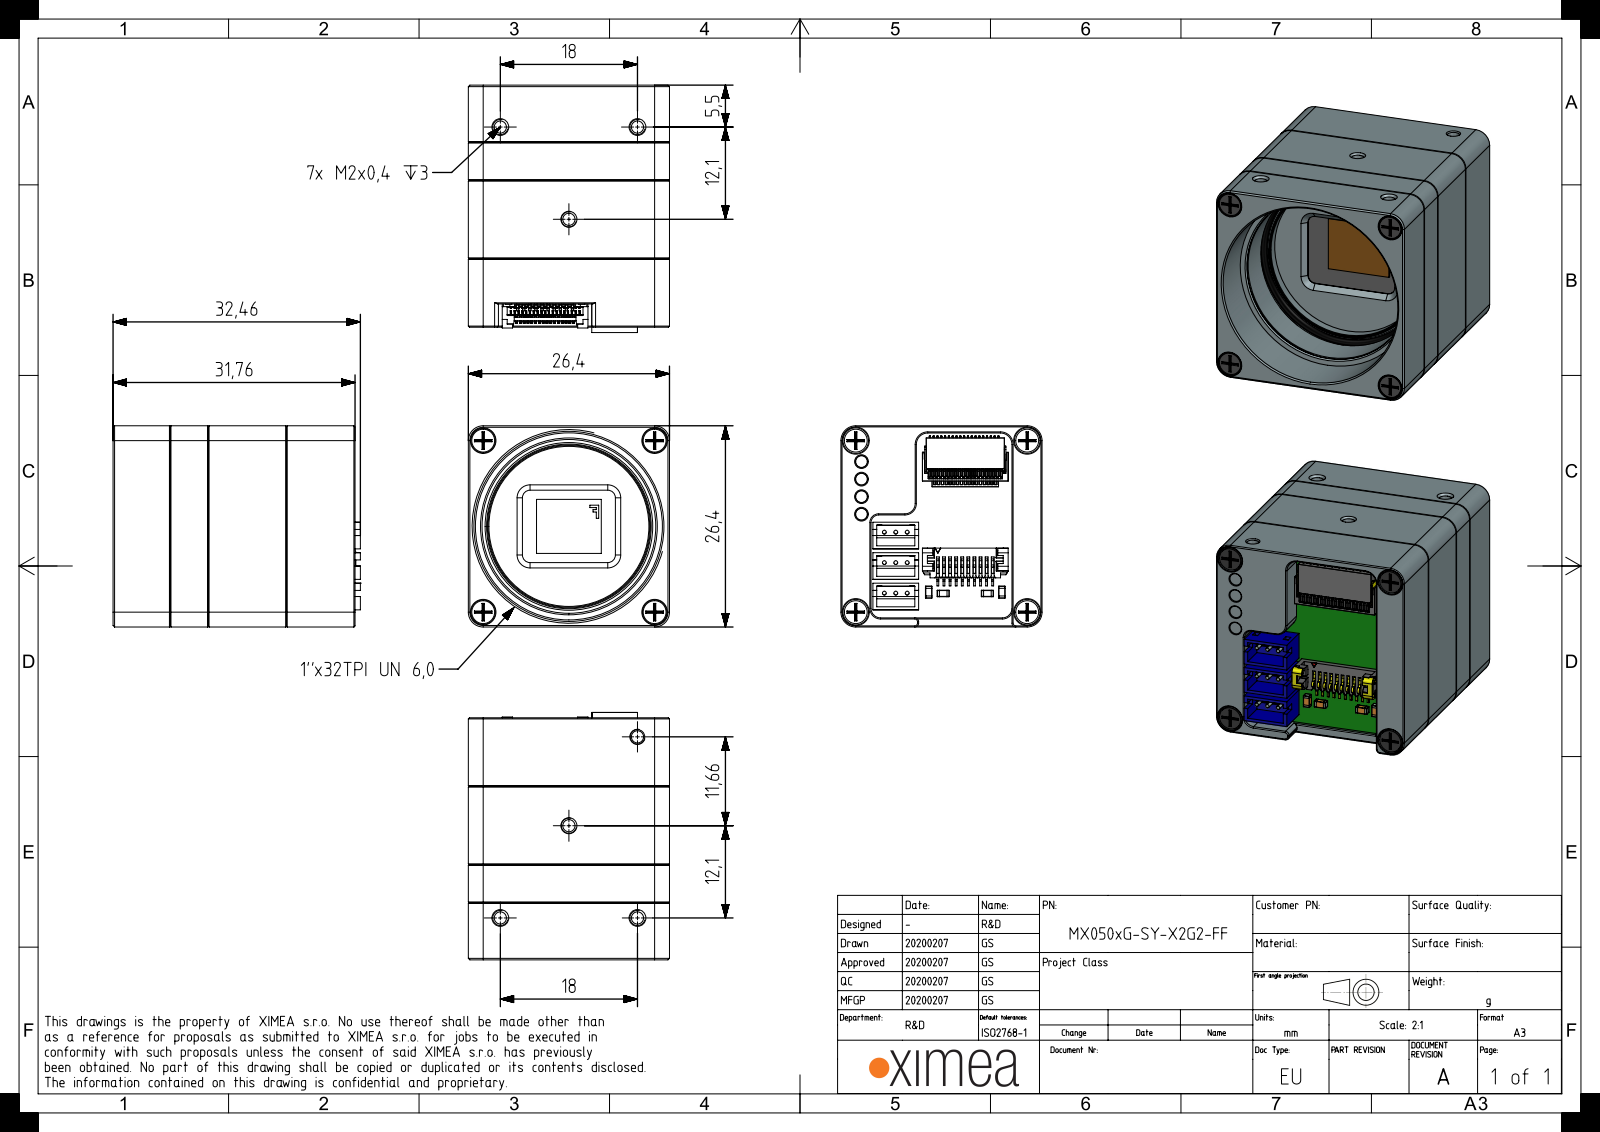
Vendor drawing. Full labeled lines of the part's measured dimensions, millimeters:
Part name (STEP PRODUCT): MX-X2G2-MAIN-FF-PCA-REV2; MECH-THERM-PAD-10X5X1; SROB-M2x4-CUST; MX-X2G2-CONN-FF-PCA (+8 more)
STEP written by: SIEMENS PLM Software NX 1907 (AUTOMOTIVE_DESIGN)
Units: millimetres
Bodies: 306 solids, 20238 faces (11952 planar, 5731 cylindrical, 2555 other)
Overall size (bounding box): 32.5 × 26.4 × 26.4
Volume: 11 500 mm³ · Surface area: 22 990 mm²
Round holes (diameter × count): ⌀1.6 ×16, ⌀0.7 ×9, ⌀2 ×8, ⌀0.9 ×4, ⌀0.9 ×4, ⌀1.8 ×4, ⌀2.1 ×4, ⌀3 ×4, ⌀3.2 ×4, ⌀3.4 ×4, ⌀0.3 ×3, ⌀0.6 ×2
Round bosses / shafts (diameter × count): ⌀0.5 ×9, ⌀1.9 ×8, ⌀3 ×6, ⌀1.6 ×4, ⌀0.8 ×4, ⌀1.6 ×2, ⌀0.8 ×2, ⌀25 ×1
Partial cylindrical surfaces — rounded edges, fillets, slot ends (radius × count): R0.1 ×77, R0.1 ×74, R0.2 ×30, R0.3 ×30, R0.4 ×27, R1.5 ×22, R1 ×18, R0.2 ×15
Main face-to-face distances: 1, 3.5, 26.4, 4.5, 4.2, 6.9, 11.4, 10.4, 7.7, 5.7
Hole centre spacings: 15.9, 1.5, 3.8, 4.3, 12.9, 13.1, 18.2, 18.8
